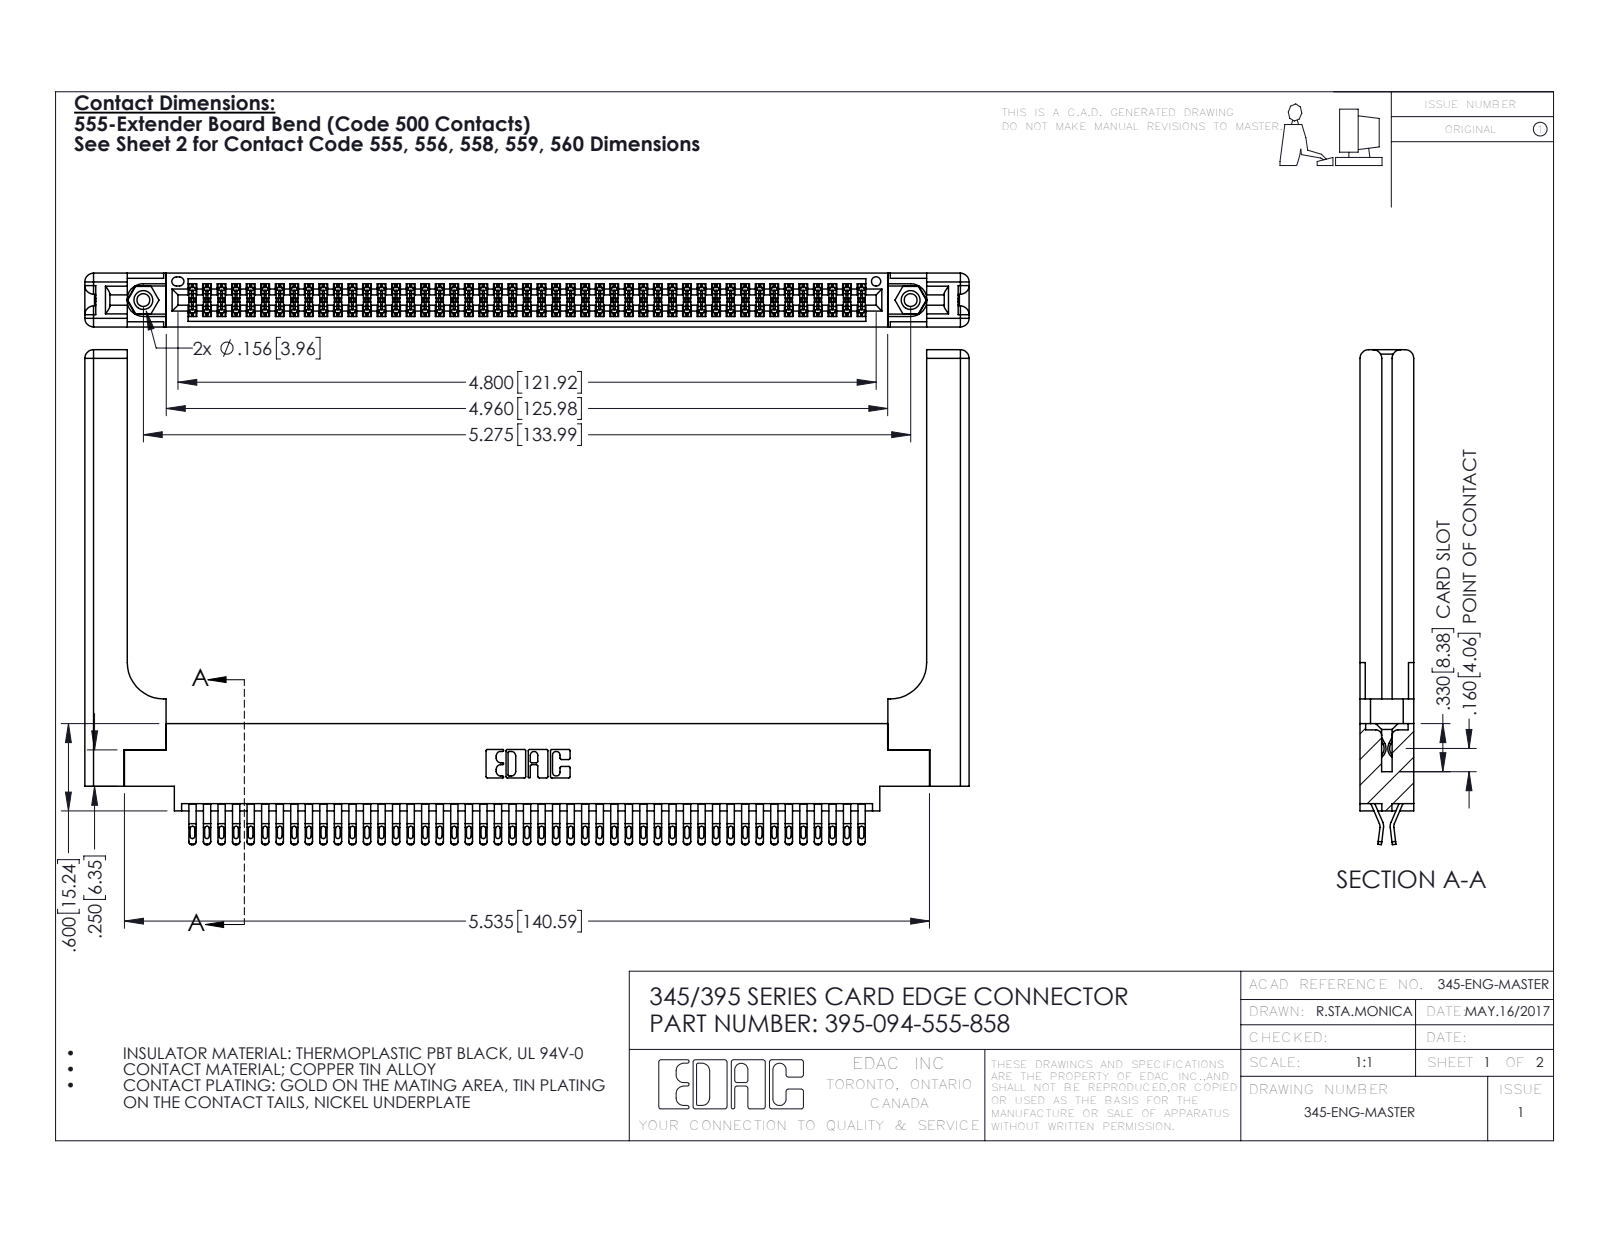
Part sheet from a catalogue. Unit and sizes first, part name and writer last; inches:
Units: inches
Overall size (bounding box): 6.079 × 3.402 × 0.37
Round holes (diameter × count): ⌀0.089 ×2, ⌀0.125 ×2, ⌀0.156 ×2, ⌀0.064 ×1
Round bosses / shafts (diameter × count): ⌀0.155 ×2
Partial cylindrical surfaces — rounded edges, fillets, slot ends (radius × count): R0.016 ×235, R0.02 ×188, R0.006 ×141, R0.01 ×22, R0.06 ×16, R0.007 ×6, R0.031 ×6, R0.026 ×3
Main face-to-face distances: 0.072, 0.37, 0.298, 0.025, 0.098, 0.272, 0.2, 0.225, 0.148, 0.15
Hole centre spacings: 0.27, 5.039, 5.275
Volume: 1.445 in³ · Surface area: 44.52 in²
Bodies: 99 solids, 5650 faces (3146 planar, 2444 cylindrical, 60 other)
Part name (STEP PRODUCT): 345-292-001_555 Tail; 345 Part_0.170 Offset - 0.156 Dia-TH; 345-220-058_345-220-058; 345-250-001_345-250-001-102 (+1 more)
STEP written by: SolidWorks 2016 (CONFIG_CONTROL_DESIGN)
